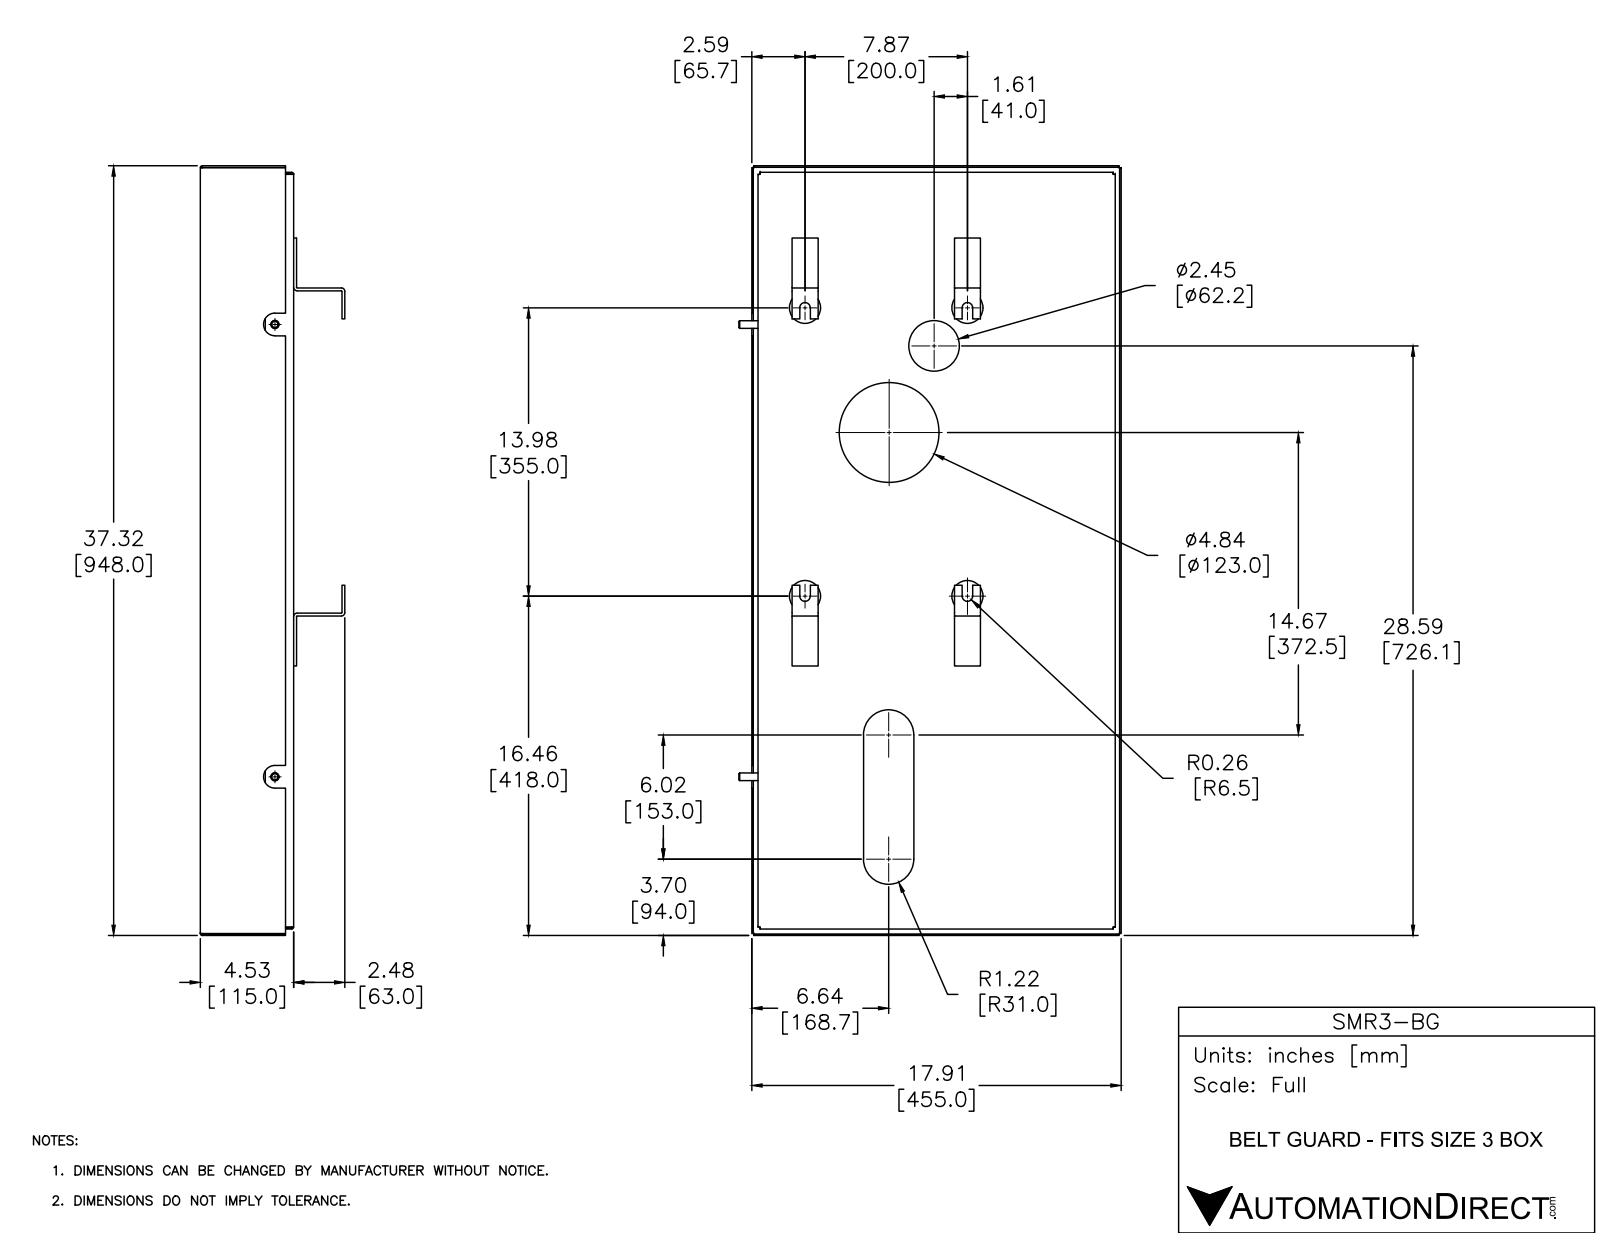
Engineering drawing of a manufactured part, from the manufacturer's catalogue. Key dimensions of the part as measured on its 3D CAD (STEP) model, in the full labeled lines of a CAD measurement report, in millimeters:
Part name (STEP PRODUCT): SMR3-BG
STEP written by: SolidWorks 2016 (AUTOMOTIVE_DESIGN)
Units: millimetres
Bodies: 10 solids, 214 faces (130 planar, 64 cylindrical, 20 other)
Overall size (bounding box): 948 × 478 × 178
Volume: 1 605 000 mm³ · Surface area: 1 750 000 mm²
Round holes (diameter × count): ⌀38.5 ×4, ⌀10 ×2, ⌀62.2 ×1, ⌀123 ×1
Round bosses / shafts (diameter × count): ⌀9.5 ×2, ⌀19 ×1
Partial cylindrical surfaces — rounded edges, fillets, slot ends (radius × count): R0.7 ×12, R2.5 ×8, R4.2 ×4, R6.5 ×4, R14 ×2, R31 ×2
Main face-to-face distances: 1.8, 453.2, 113.2, 455, 451.4, 946.2, 115, 111.4, 7.7, 445.5
Hole centre spacings: 200, 355, 407.5, 62.3, 120.2, 165.8, 181.3, 185.1
